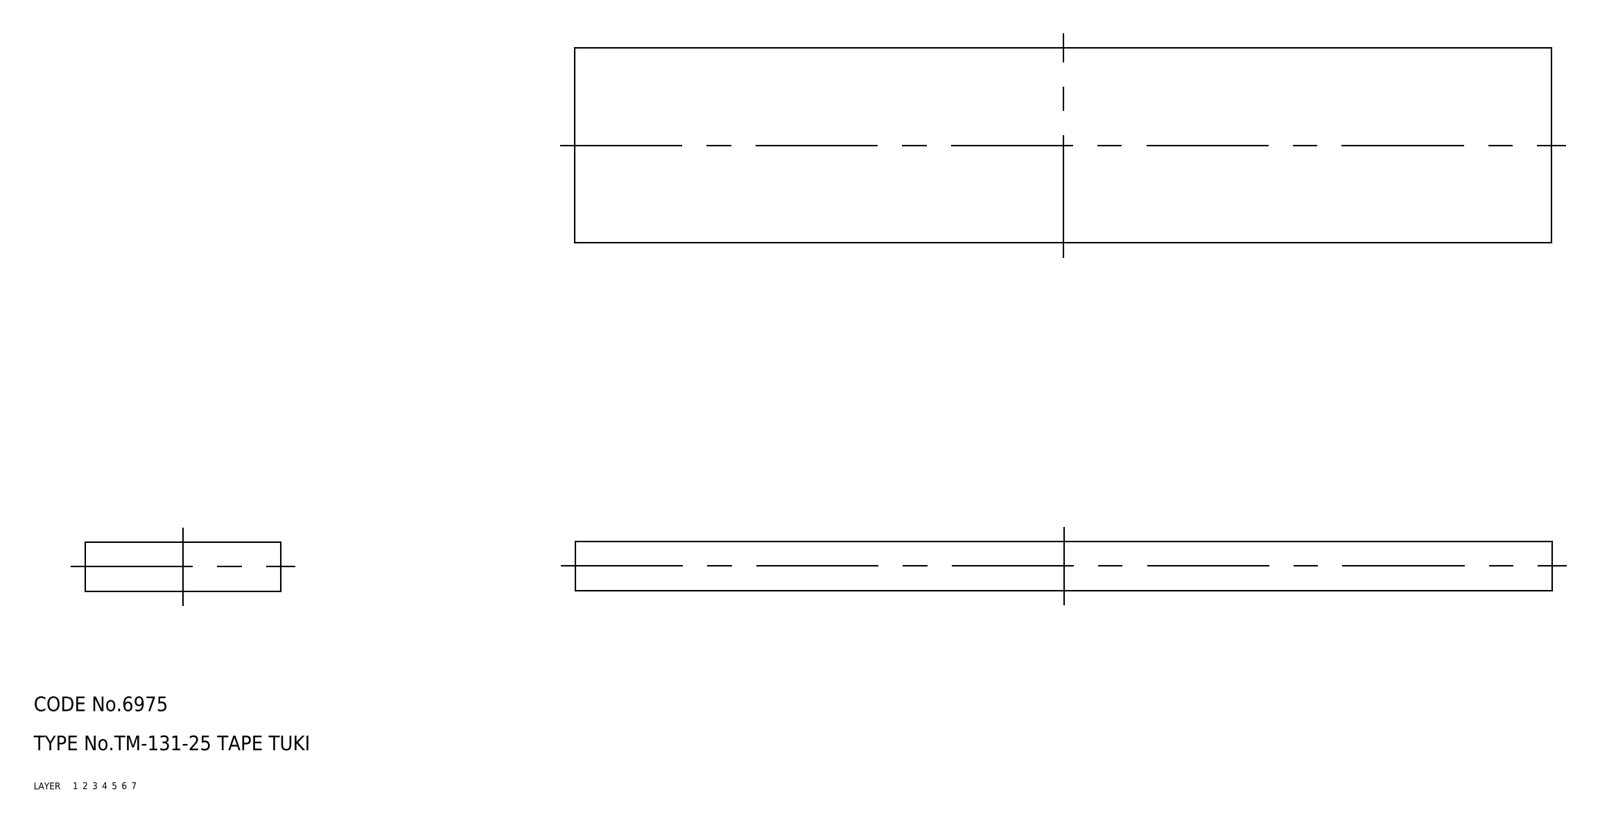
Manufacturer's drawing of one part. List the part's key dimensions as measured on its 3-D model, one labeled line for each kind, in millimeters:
Part name (STEP PRODUCT): rubber foam
STEP written by: CADfix (AUTOMOTIVE_DESIGN)
Units: millimetres
Bodies: 1 solid, 6 faces (0 planar, 0 cylindrical, 6 other)
Overall size (bounding box): 200 × 40 × 10
Volume: 80 000 mm³ · Surface area: 20 800 mm²
